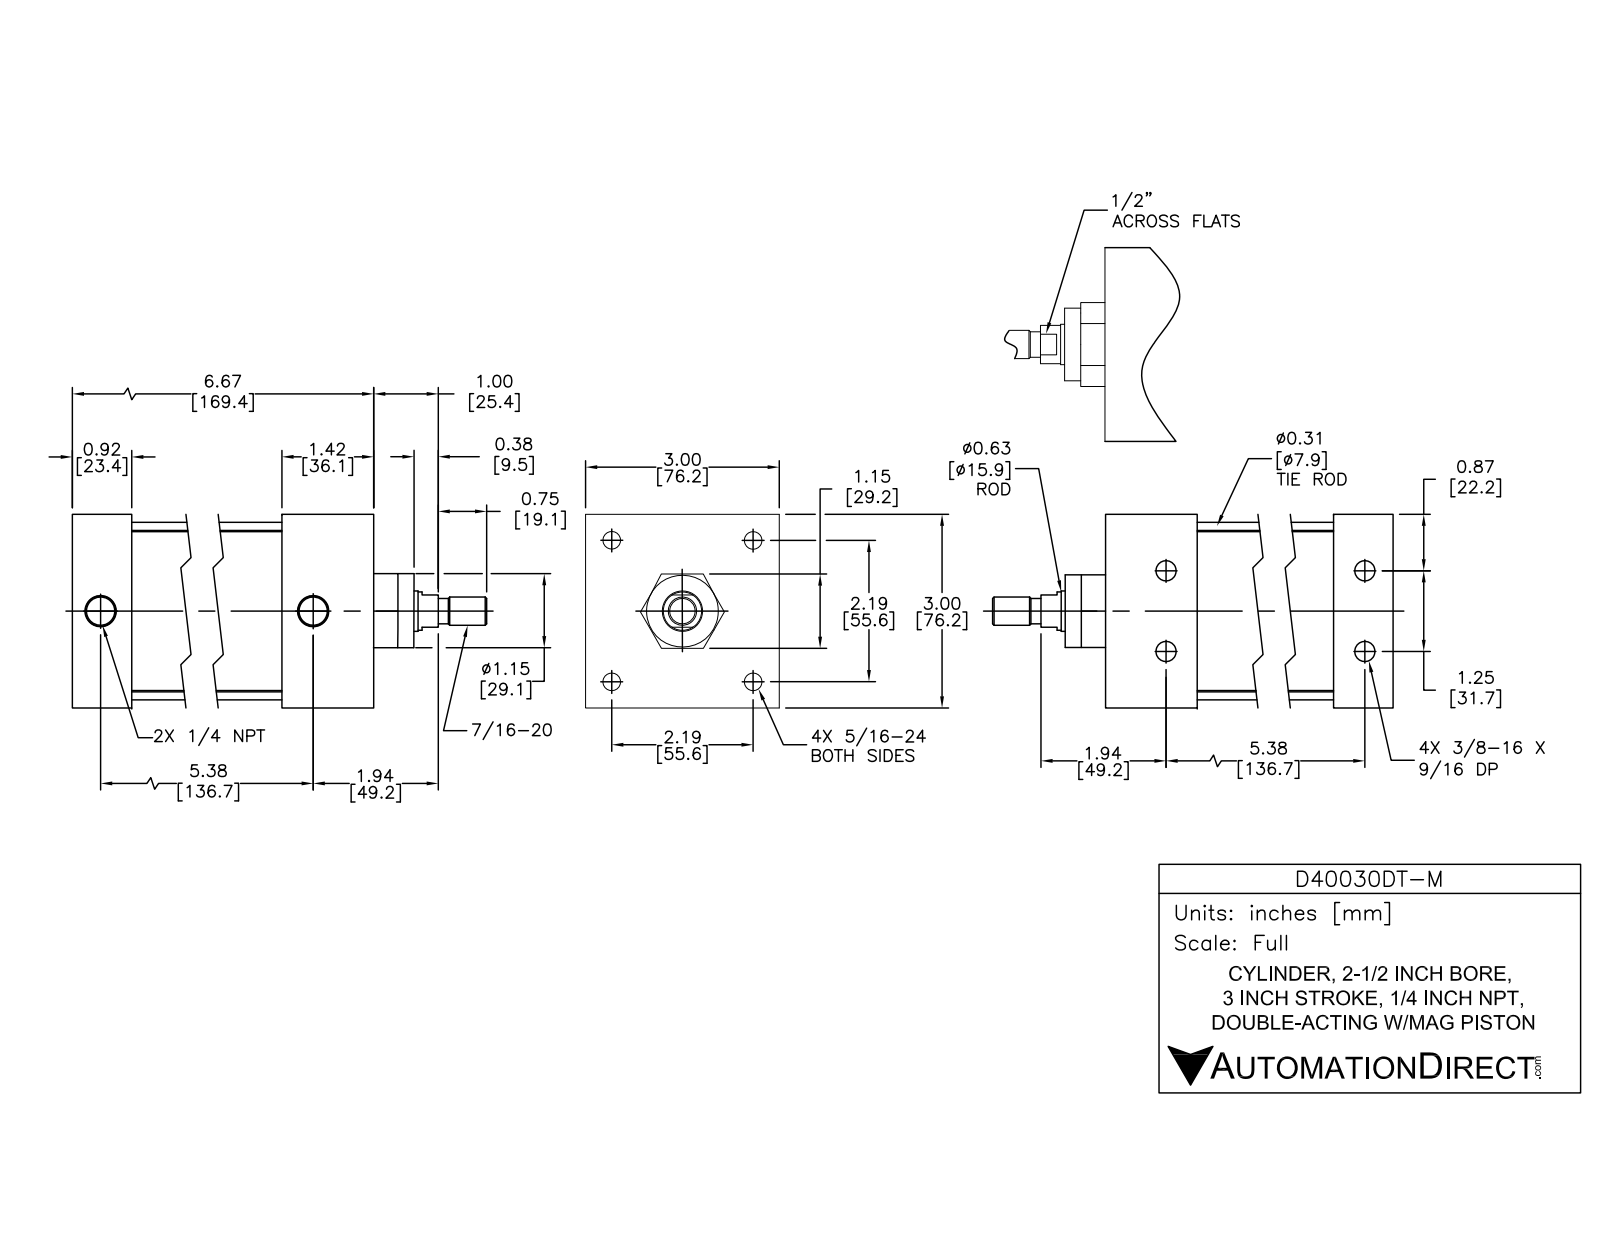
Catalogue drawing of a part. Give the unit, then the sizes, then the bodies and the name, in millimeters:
Units: millimetres
Overall size (bounding box): 215.8 × 76.2 × 76.2
Round holes (diameter × count): ⌀6.8 ×4, ⌀7.8 ×4, ⌀9.1 ×4, ⌀12.7 ×4, ⌀7.5 ×2, ⌀12.1 ×2, ⌀15.9 ×1, ⌀16 ×1, ⌀63.5 ×1
Round bosses / shafts (diameter × count): ⌀12.3 ×4, ⌀8 ×4, ⌀7.2 ×4, ⌀69.9 ×1, ⌀63.4 ×1, ⌀28.4 ×1, ⌀15.8 ×1, ⌀15 ×1
Partial cylindrical surfaces — rounded edges, fillets, slot ends (radius × count): R7.6 ×4
Main face-to-face distances: 76.2, 2, 109.9, 171.3, 145.4, 25.9, 36.1, 109.4, 135.3, 25.4
Hole centre spacings: 39.5, 55.9, 137.3, 136.4, 15.9, 15.9, 31.8, 79
Volume: 556 700 mm³ · Surface area: 141 100 mm²
Bodies: 12 solids, 298 faces (94 planar, 114 cylindrical, 90 other)
Part name (STEP PRODUCT): D40030DT-M PISTON; D40030DT-M; D40030DT-M BODY
STEP written by: SolidWorks 2015 (AUTOMOTIVE_DESIGN)
